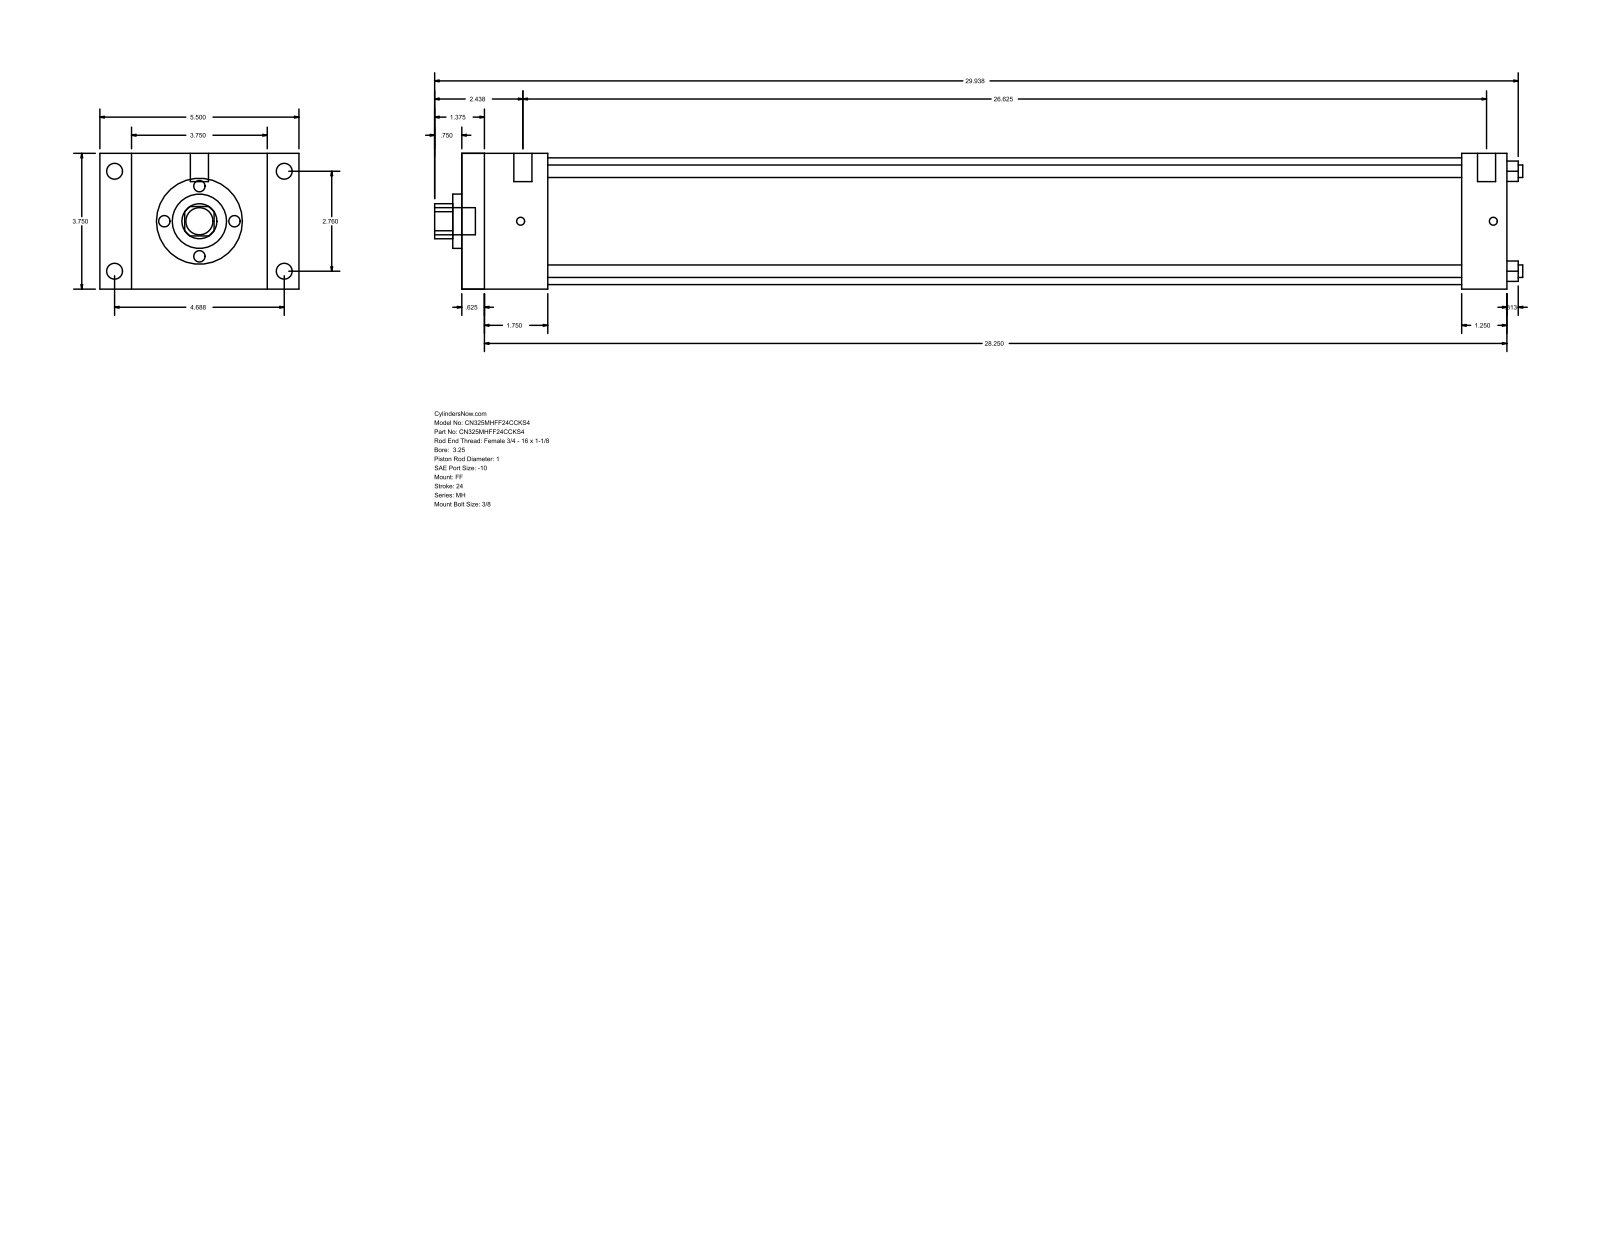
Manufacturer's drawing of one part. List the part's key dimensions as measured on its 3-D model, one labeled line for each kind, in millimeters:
Part name (STEP PRODUCT): MH_FF__0325_1
STEP written by: GSSL Pune (CONFIG_CONTROL_DESIGN)
Units: millimetres
Bodies: 0 solids, 92 faces (64 planar, 28 cylindrical, 0 other)
Overall size (bounding box): 763.59 × 139.7 × 95.25
Round holes (diameter × count): ⌀8.76 ×4, ⌀25.4 ×1, ⌀38.1 ×1, ⌀88.9 ×1
Round bosses / shafts (diameter × count): ⌀11.13 ×4, ⌀5.56 ×4, ⌀12.7 ×2, ⌀19.05 ×1
Partial cylindrical surfaces — rounded edges, fillets, slot ends (radius × count): R12.29 ×1
Main face-to-face distances: 95.24, 733.43, 15.87, 717.56, 22.23, 117.47, 701.68, 685.81, 31.75, 60.33
Hole centre spacings: 49.57, 70.1, 99.14
